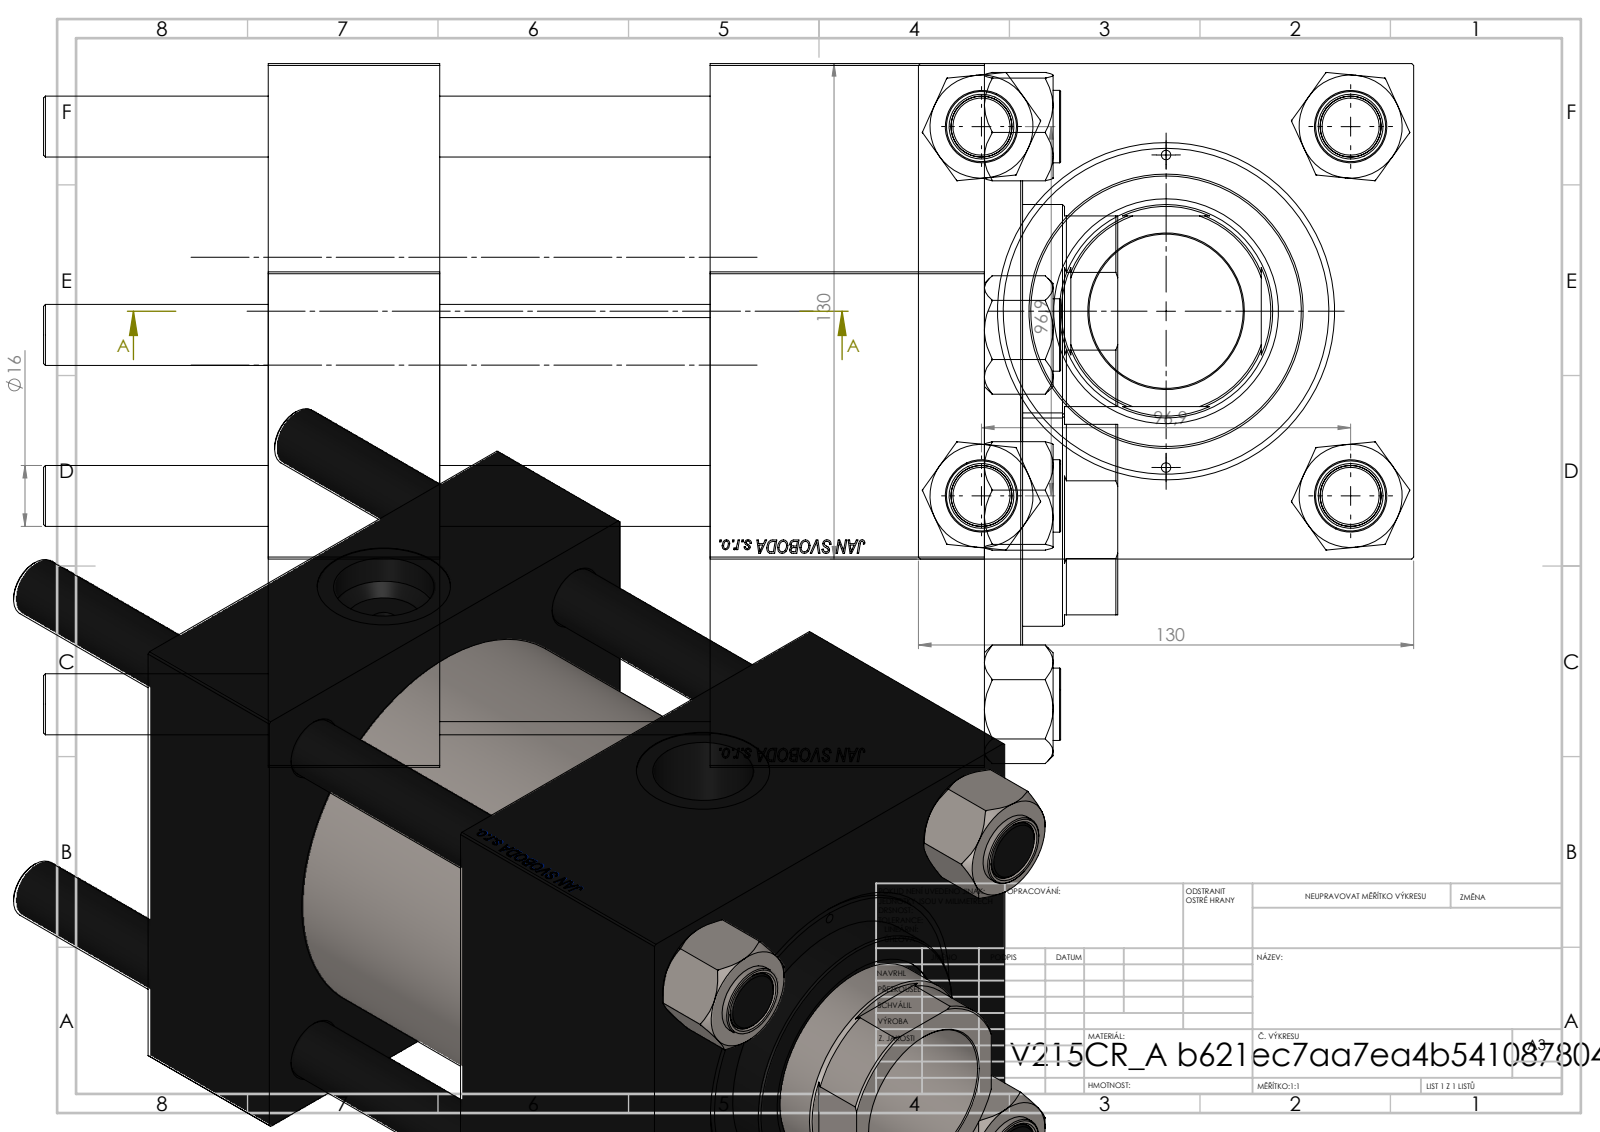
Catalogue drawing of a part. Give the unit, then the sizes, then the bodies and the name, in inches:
Units: inches
Overall size (bounding box): 11.102 × 5.118 × 5.118
Round holes (diameter × count): ⌀0.63 ×4, ⌀0.098 ×2, ⌀0.276 ×2, ⌀1.041 ×2, ⌀1.378 ×2, ⌀1.594 ×1, ⌀2.205 ×1, ⌀2.323 ×1, ⌀2.992 ×1, ⌀3.366 ×1, ⌀3.937 ×1
Round bosses / shafts (diameter × count): ⌀0.748 ×4, ⌀4.173 ×1, ⌀2.835 ×1
Partial cylindrical surfaces — rounded edges, fillets, slot ends (radius × count): R1.063 ×1
Main face-to-face distances: 5.118, 1.772, 7.402, 5.63, 4.567, 2.795, 2.835, 0.787, 3.622, 3.78
Hole centre spacings: 1.93, 2.698, 3.815, 4.005, 1.614, 5.395, 3.228, 4.665
Volume: 155.4 in³ · Surface area: 559.9 in²
Bodies: 11 solids, 1186 faces (568 planar, 82 cylindrical, 536 other)
Part name (STEP PRODUCT): V215_VC_A; V215CR_BODY_A; CR025_012_A_0_G_A_G_M_020_+#_##_TYCINKA; V215CR_VCP (+1 more)
STEP written by: SolidWorks 2019 (CONFIG_CONTROL_DESIGN)
